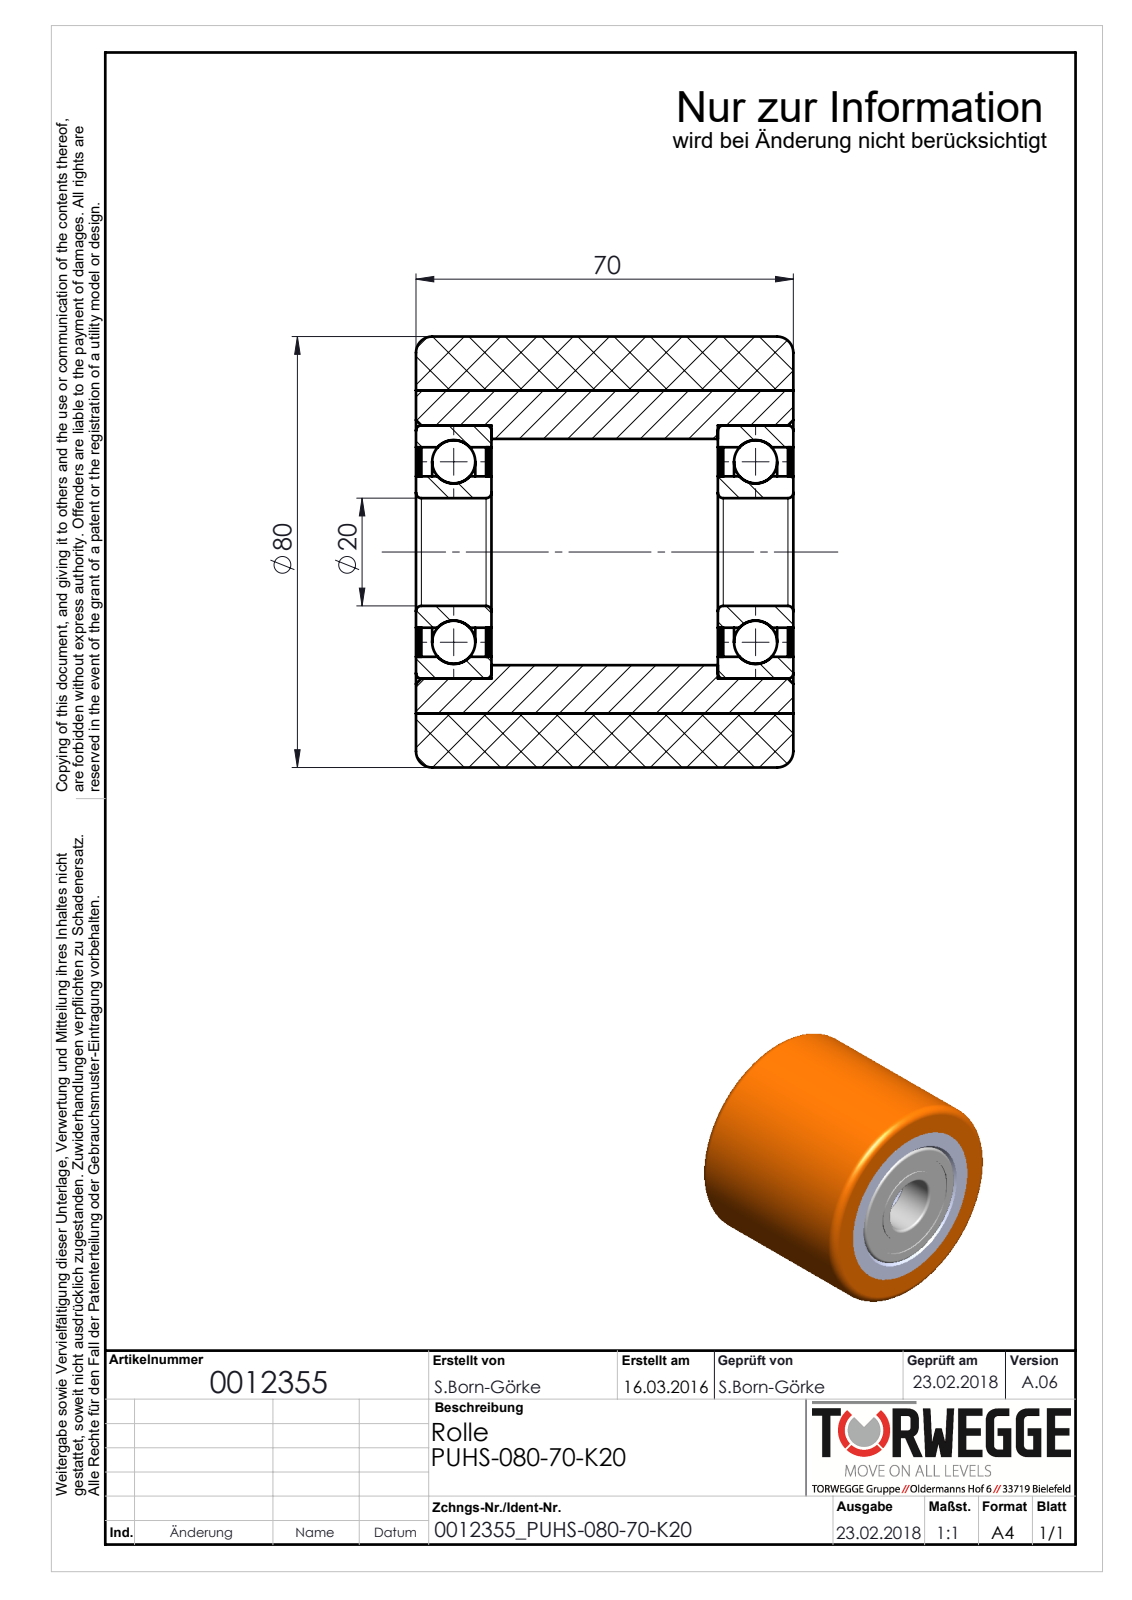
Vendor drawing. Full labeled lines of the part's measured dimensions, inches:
Part name (STEP PRODUCT): 0012355_PUHS-080-70-K20
STEP written by: SolidWorks 2016 (AUTOMOTIVE_DESIGN)
Units: inches
Bodies: 12 solids, 118 faces (22 planar, 52 cylindrical, 44 other)
Overall size (bounding box): 3.15 × 3.15 × 2.756
Volume: 16.9 in³ · Surface area: 132.6 in²
Round holes (diameter × count): ⌀0.787 ×1, ⌀1.106 ×1, ⌀1.531 ×1, ⌀1.654 ×1, ⌀1.85 ×1, ⌀2.362 ×1
Round bosses / shafts (diameter × count): ⌀3.15 ×1
Main face-to-face distances: 0.02, 2.205, 0.512, 2.756, 0.039, 0.531, 2.224, 0.492, 2.185, 0.551
